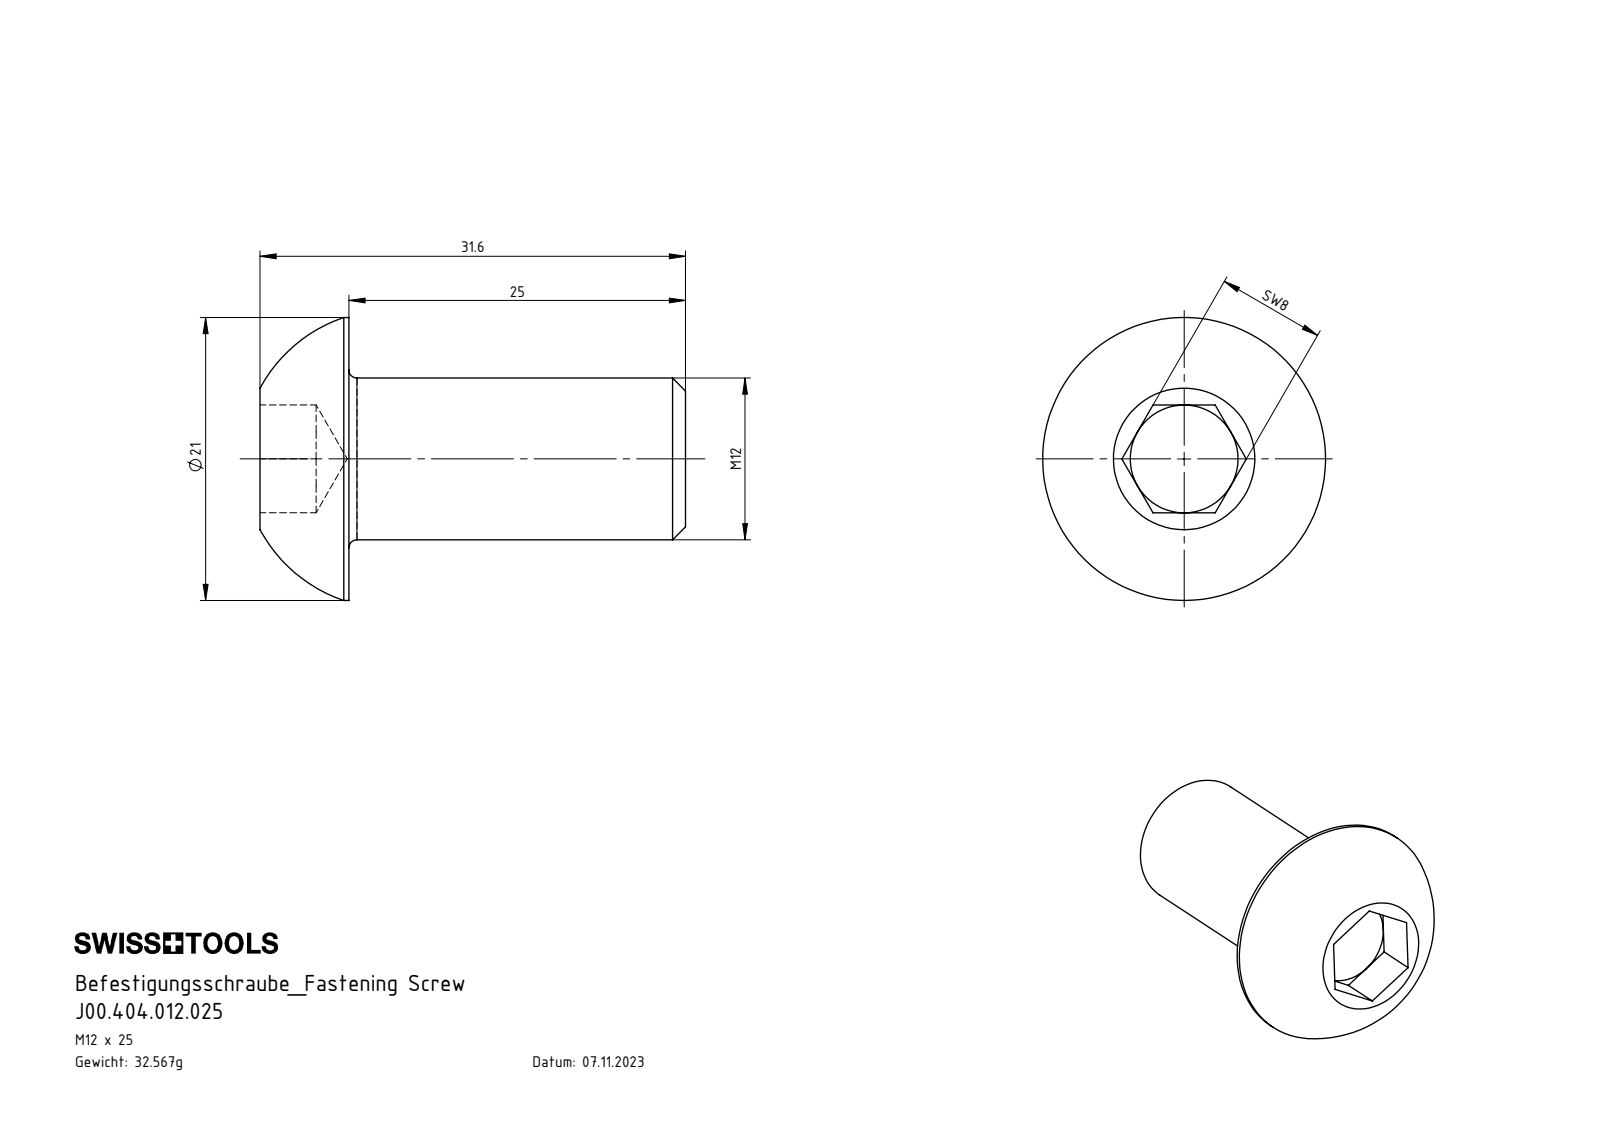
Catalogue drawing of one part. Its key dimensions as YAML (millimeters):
part_name: "J00.404.012.025"
step_written_by: "SolidWorks 2022 (AUTOMOTIVE_DESIGN)"
units: millimeters
bodies: {solids: 1, faces: 27, planar: 15, cylindrical: 4, other: 8}
overall_size: [31.6, 21, 21]
volume: 4149
surface_area: 1925
round_bosses_or_shafts:
  - {diameter: 21, count: 1}
  - {diameter: 12, count: 1}
face_to_face_distances: [25, 8, 6.6, 31.6, 4.16, 2.44, 27.44]
